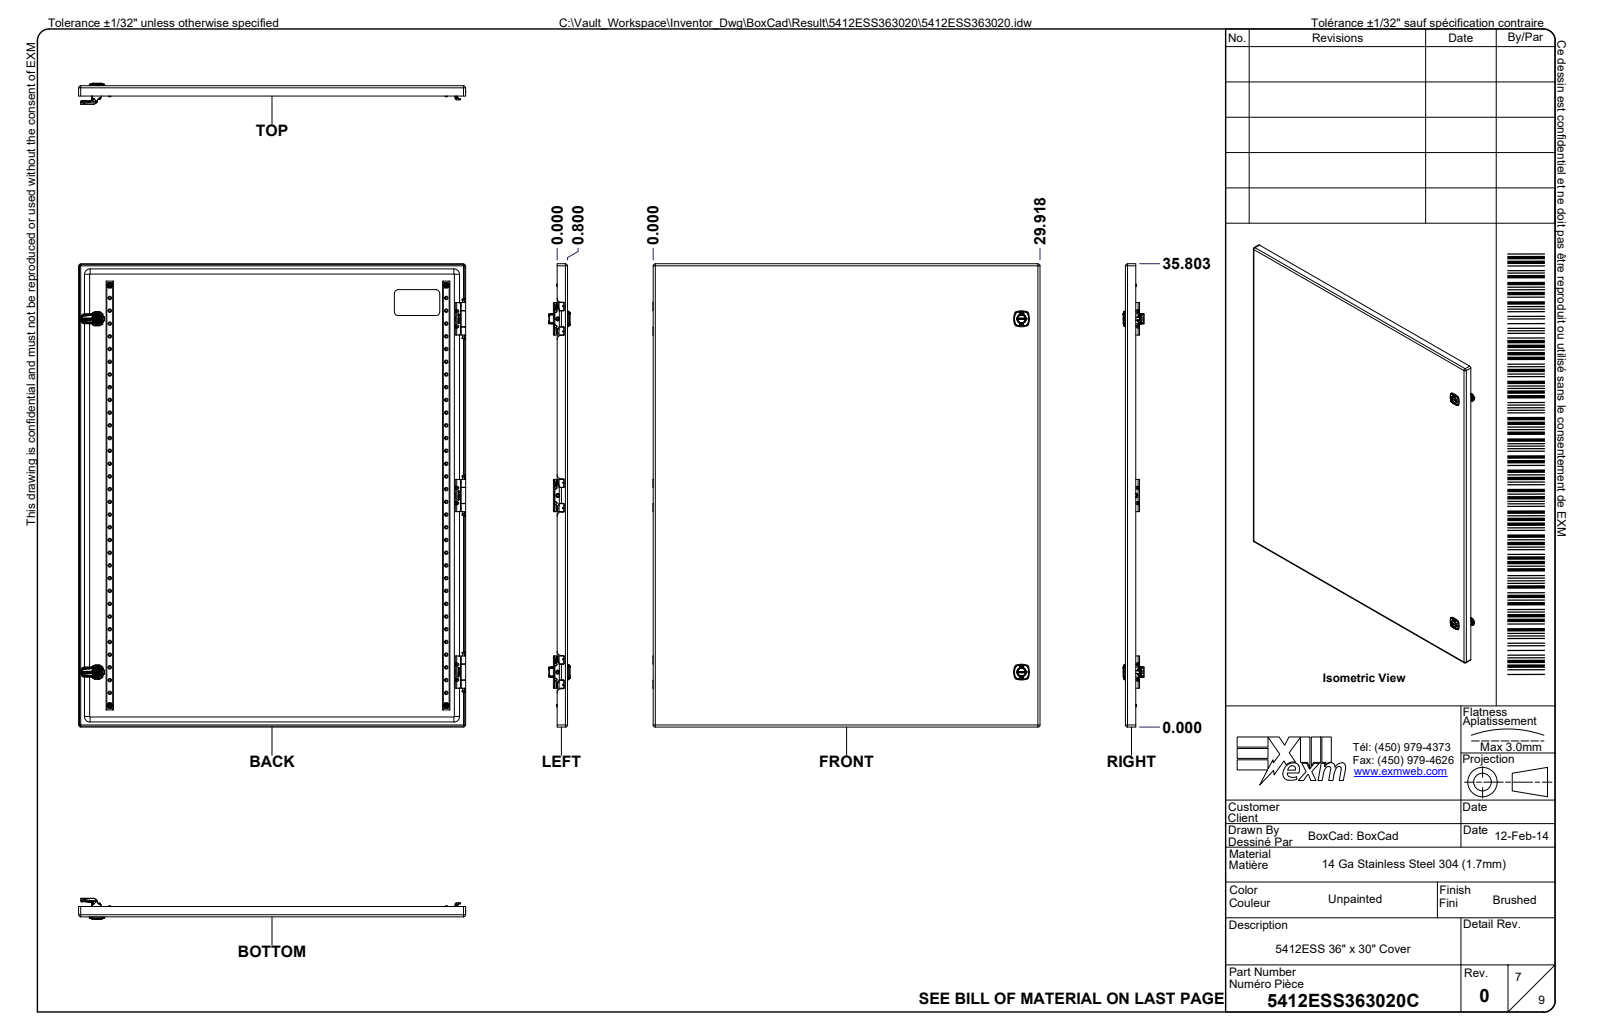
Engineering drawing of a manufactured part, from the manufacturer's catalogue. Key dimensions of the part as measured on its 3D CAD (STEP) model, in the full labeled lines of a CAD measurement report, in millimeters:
Part name (STEP PRODUCT): 5412ESS363020; 5412ESS363020B; 5412ESS363020B-P; STK-Q-16020 (+8 more)
STEP written by: Autodesk Inventor 2024 (AUTOMOTIVE_DESIGN)
Units: millimetres
Bodies: 78 solids, 11498 faces (3667 planar, 2466 cylindrical, 5365 other)
Overall size (bounding box): 914.4 × 762.2 × 540.8
Volume: 7 713 000 mm³ · Surface area: 8 213 000 mm²
Round holes (diameter × count): ⌀4.2 ×64, ⌀0.8 ×11, ⌀8 ×10, ⌀5.1 ×9, ⌀7.4 ×7, ⌀1.1 ×6, ⌀6.9 ×6, ⌀7.9 ×6, ⌀5 ×4, ⌀6.8 ×4, ⌀9.9 ×4, ⌀6 ×3
Round bosses / shafts (diameter × count): ⌀6 ×64, ⌀1 ×12, ⌀0.8 ×11, ⌀5.9 ×10, ⌀18.2 ×6, ⌀7.9 ×6, ⌀6.7 ×6, ⌀9.5 ×4
Partial cylindrical surfaces — rounded edges, fillets, slot ends (radius × count): R0.5 ×106, R1 ×92, R0.2 ×86, R0.3 ×34, R0.8 ×34, R0.3 ×28, R2.5 ×24, R3.2 ×22
Main face-to-face distances: 1.7, 534.7, 760.3, 912.7, 533, 536.4, 512.5, 23.9, 22.2, 510.8
Hole centre spacings: 50, 25, 75, 100, 125, 150, 175, 200
